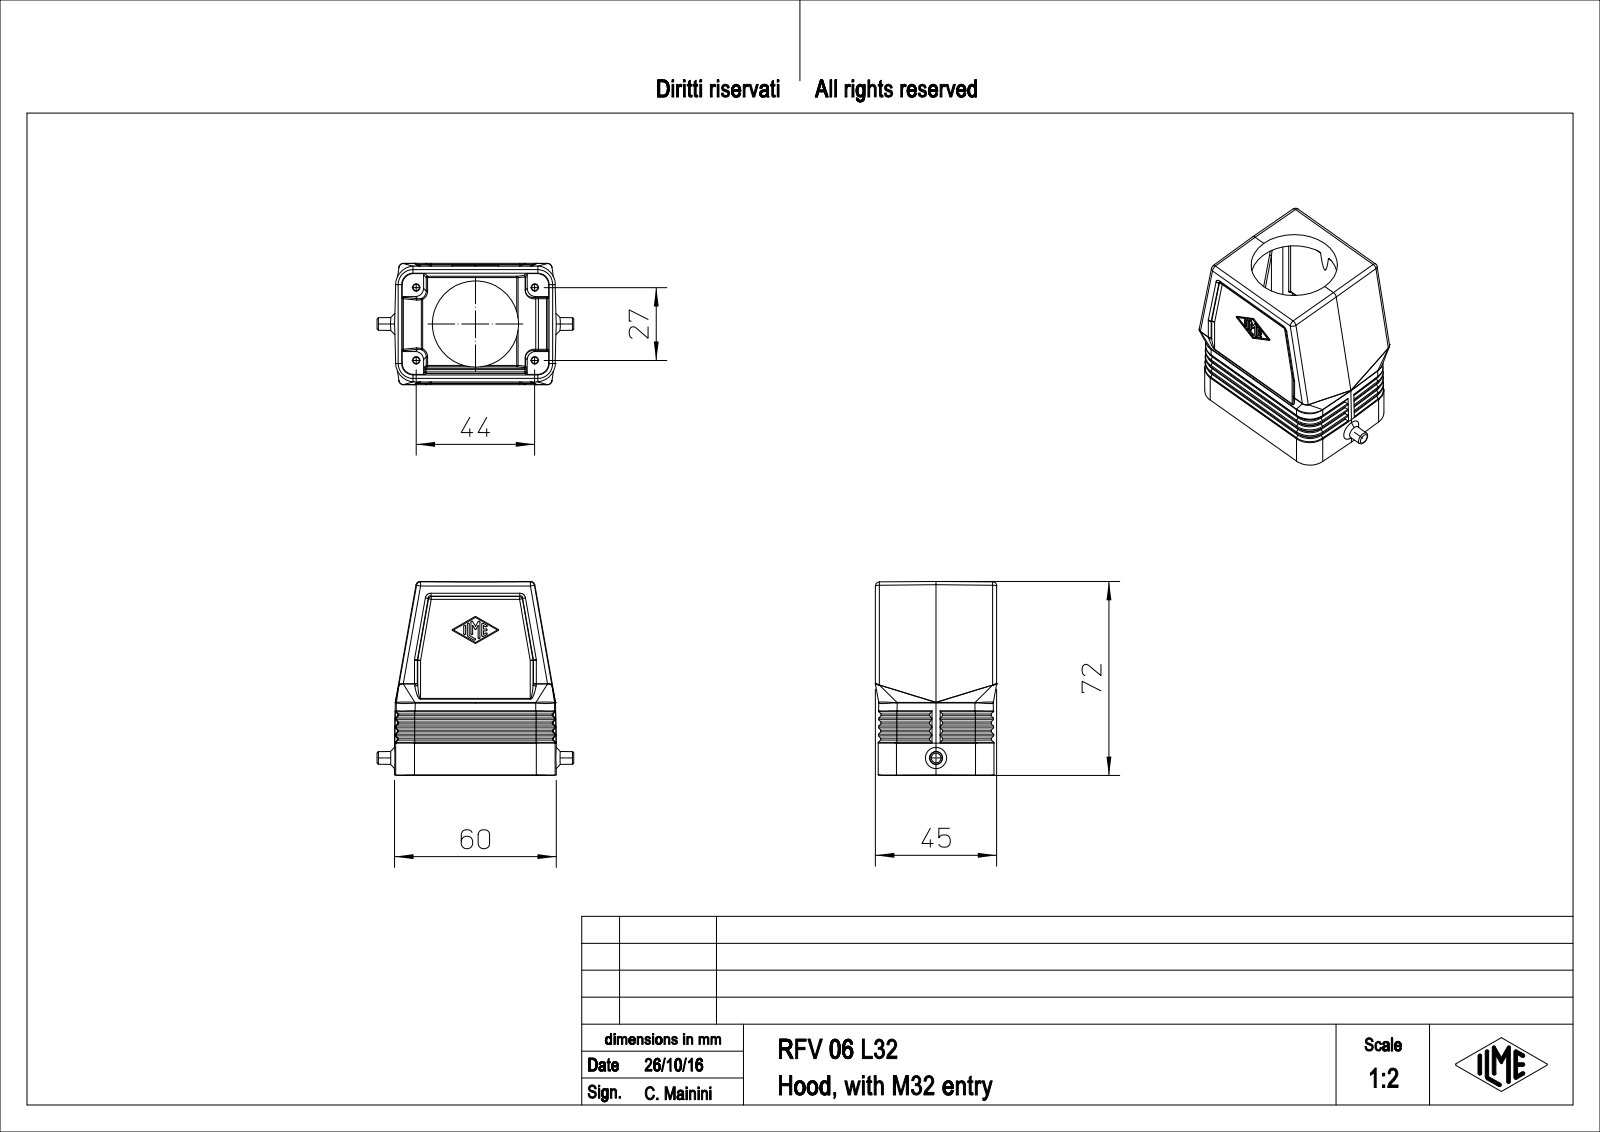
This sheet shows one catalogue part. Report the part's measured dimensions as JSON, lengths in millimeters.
{"part_name": "RFV_06_L32", "step_written_by": "PTC Creo Elements/Direct Modeling 19.0E 27-Jun-2016 (C) Parametric Technology GmbH (AUTOMOTIVE_DESIGN)", "units": "millimeters", "bodies": {"solids": 1, "faces": 381, "planar": 155, "cylindrical": 102, "other": 124}, "overall_size": [73, 72, 45], "volume_mm3": 57888, "surface_area_mm2": 28341, "round_holes": [[2.75, 4], [32, 1]], "round_bosses_or_shafts": [[4.62, 1]], "partial_cylinders_radius": [[0.5, 54], [1.5, 10], [7, 8], [3, 4], [4.2, 4]], "face_to_face_distances": [43, 1.85, 7.95, 2, 1, 44, 8.5, 4, 45, 60], "hole_center_spacings": [25.81, 27, 44, 51.62]}
